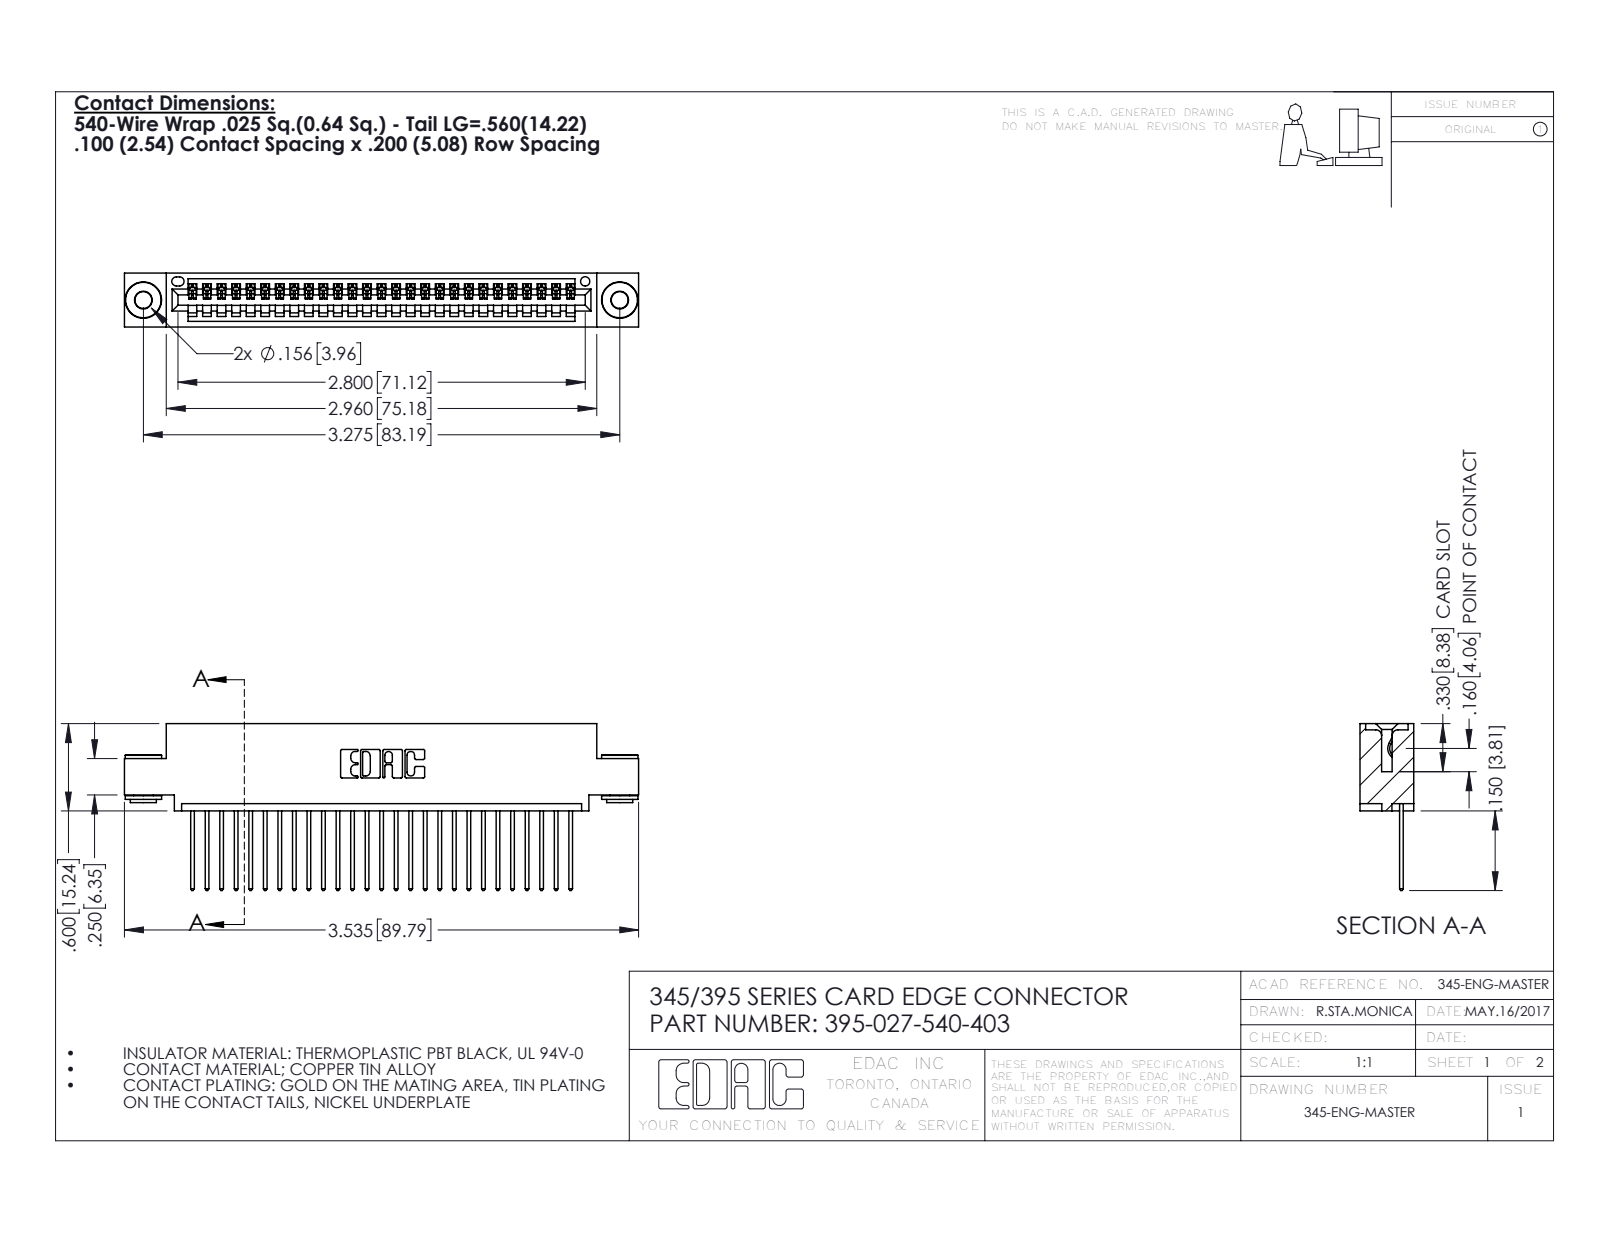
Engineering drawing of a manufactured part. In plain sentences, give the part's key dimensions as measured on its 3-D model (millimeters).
The part is named "345 Part_0.110 Offset - 0.156 Dia-TH; 395-027-540-403; 345-292-001_345-293-140; 345-250-002_345-250-002-102". Its 3-D file was written by "SolidWorks 2016 (CONFIG_CONTROL_DESIGN)". It is 30 solids with 1734 faces: 1174 planar, 552 cylindrical and 8 other. Overall it measures 89.8 by 29.1 by 9.4 millimeters. Its volume is 8 390 cubic millimeters and its surface area 11 500 square millimeters. Round holes: 2 of diameter 2.9, 2 of diameter 4, 1 of diameter 1.6. Round bosses or shafts: 2 of diameter 6.4, 2 of diameter 4.6, 2 of diameter 3.5. Partial cylindrical surfaces (rounded edges, fillets, slot ends): 54 of radius 0.2, 54 of radius 0.3, 22 of radius 0.3, 6 of radius 0.2, 6 of radius 0.8, 3 of radius 0.7, 2 of radius 0.8, 2 of radius 1. The main face-to-face distances are 1.8, 7.6, 9.4, 0.6, 5.1, 2.5, 6.9, 5.7, 3.8, 1.8. The hole center spacings are 6.9, 77.2, 83.2.
